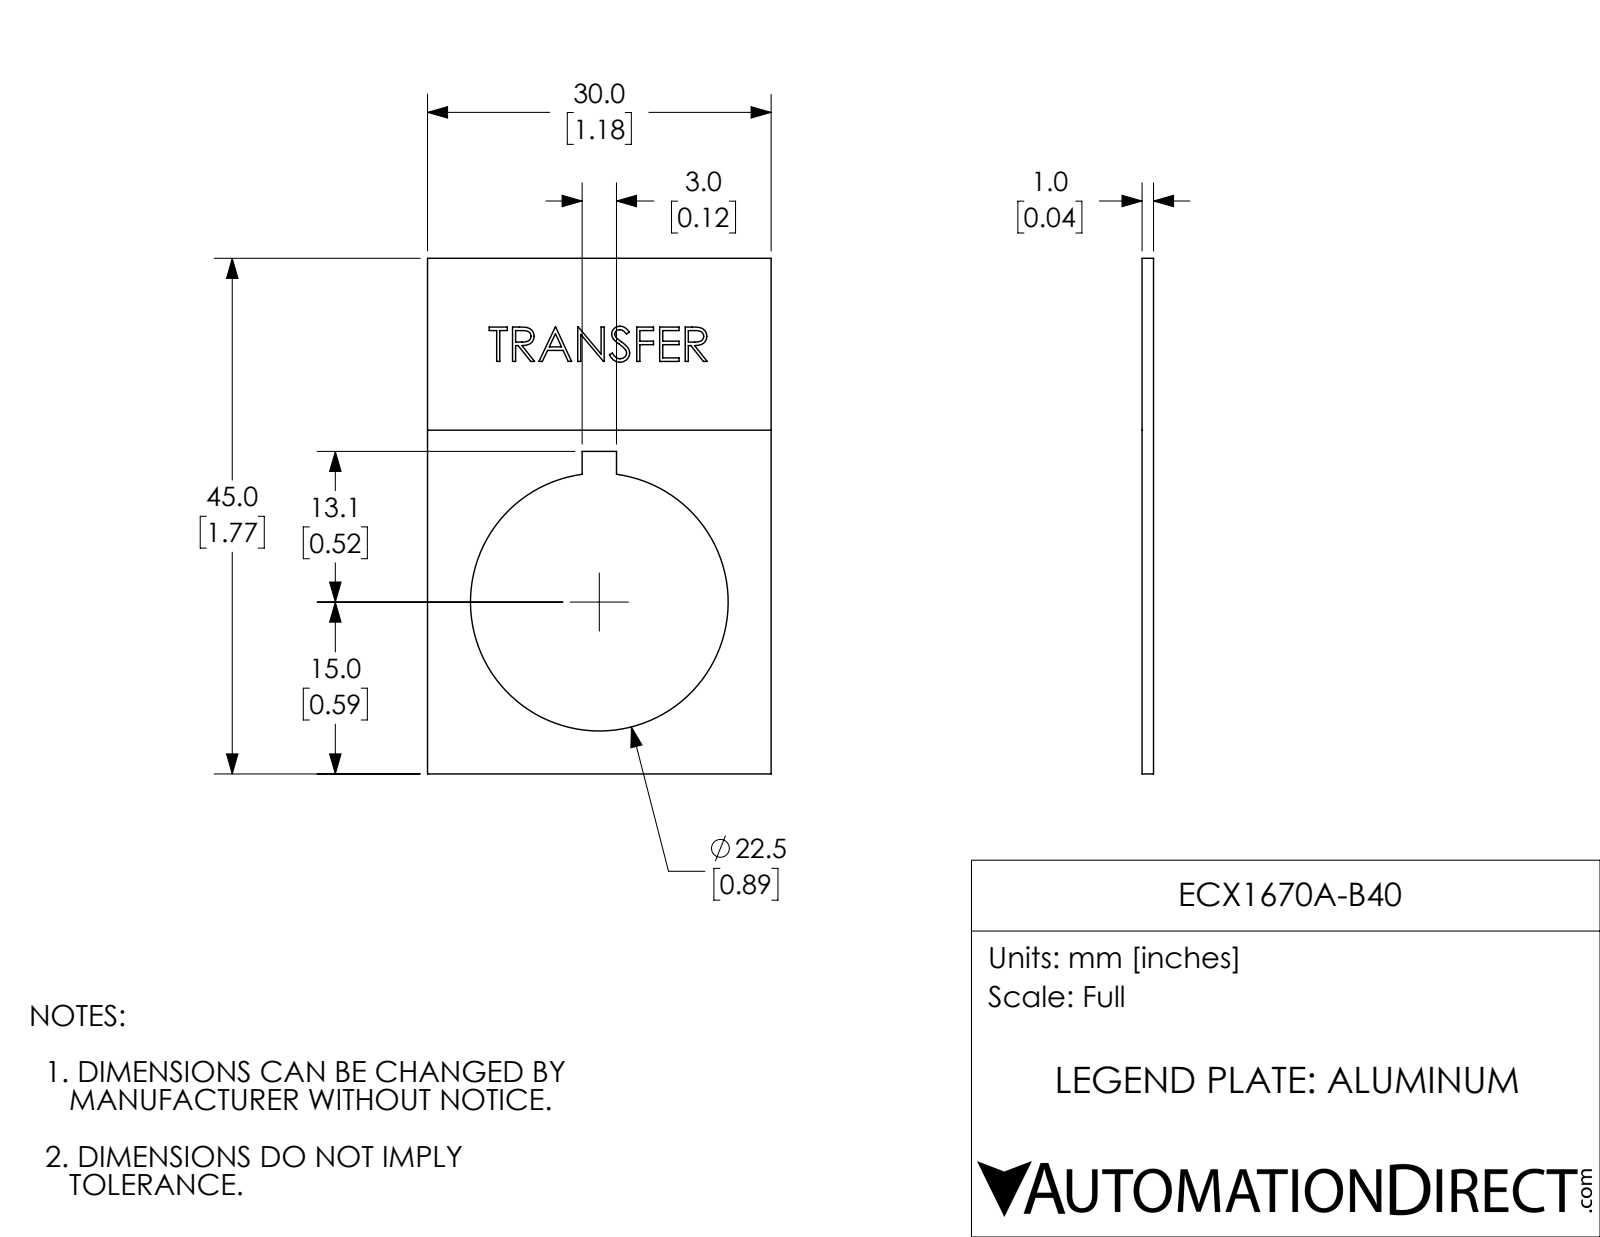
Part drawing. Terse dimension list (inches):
name: ECX1670A-B40
written by: SolidWorks 2017 (AUTOMOTIVE_DESIGN)
unit: in
bodies: 1 solid, 124 faces (96 planar, 3 cylindrical, 25 other)
size: 1.772 × 1.181 × 0.039
volume: 0.058 in³; area: 3.287 in²
holes: 1× ⌀0.886
face distances: 0.039, 1.181, 1.772, 0.038, 0.531, 0.65, 1.108, 0.663, 0.118, 0.427
